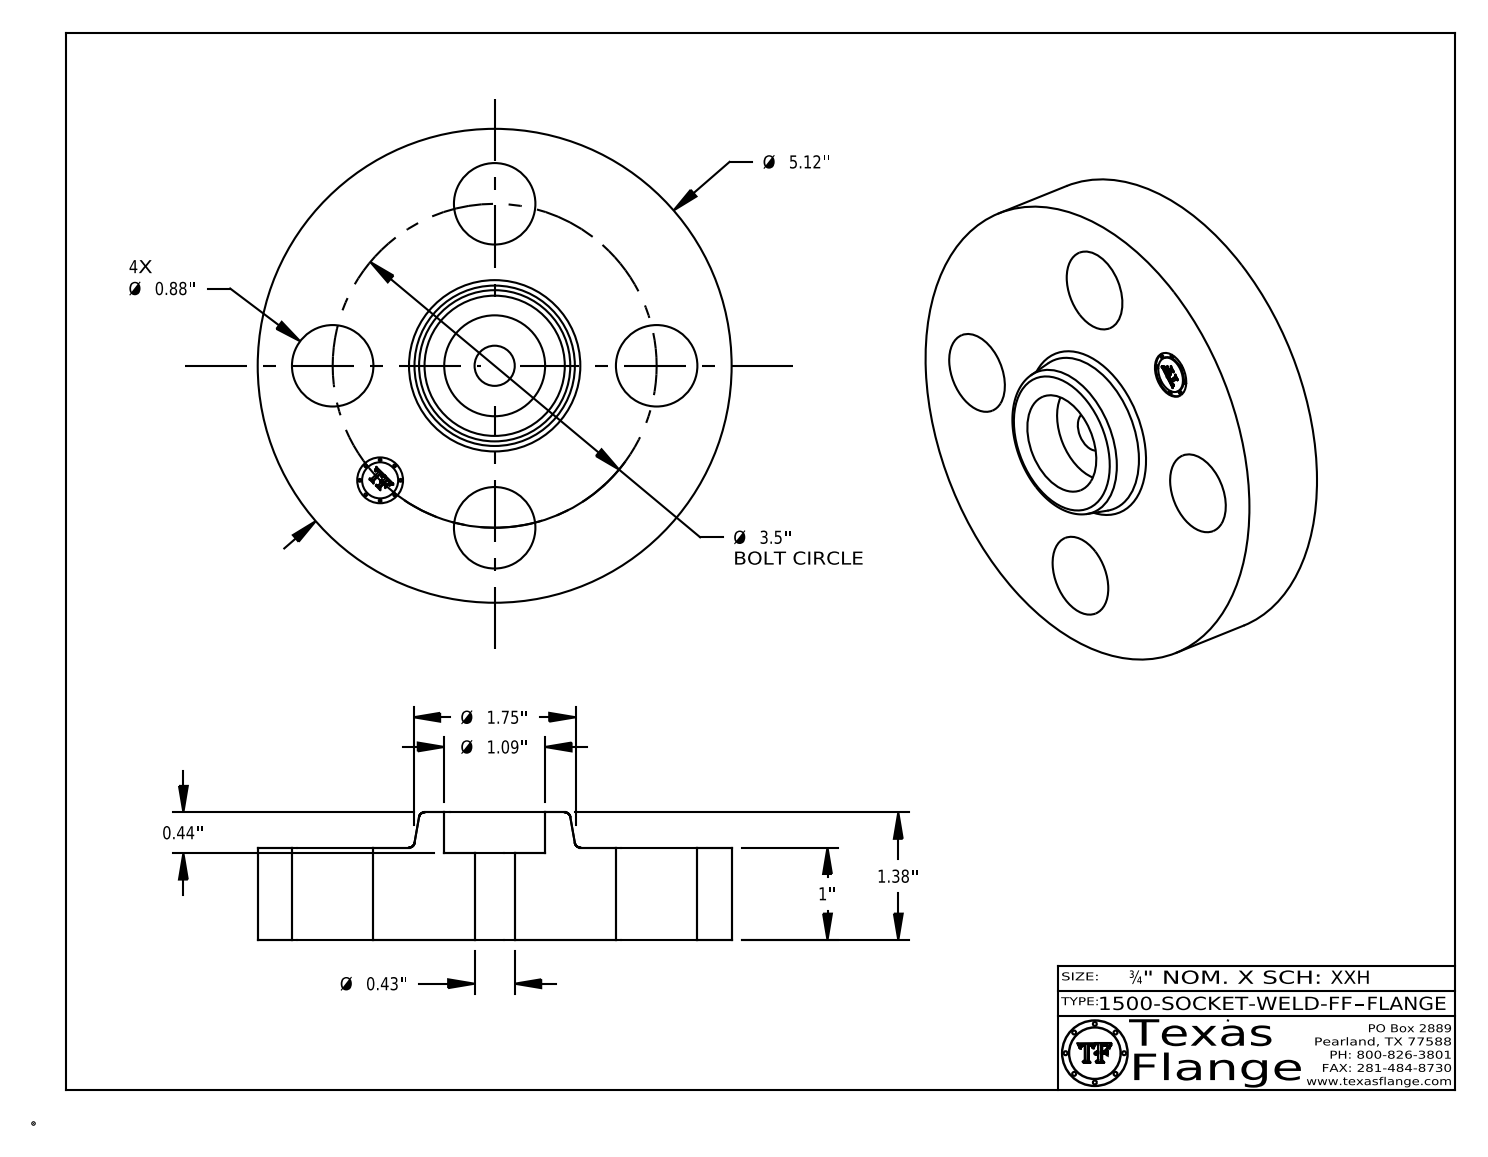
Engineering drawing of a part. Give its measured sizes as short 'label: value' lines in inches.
name: 1500-SOCKET-WELD-FF
written by: CATIA V5 STEP AP214 (AUTOMOTIVE_DESIGN)
unit: in
bodies: 1 solid, 409 faces (369 planar, 34 cylindrical, 6 other)
size: 5.12 × 5.12 × 1.38
volume: 18.45 in³; area: 67.55 in²
holes: 4× ⌀0.88, 1× ⌀0.434, 1× ⌀0.495, 1× ⌀1.09
bosses: 8× ⌀0.03, 1× ⌀5.12, 1× ⌀0.39
face distances: 1, 1.38, 0.38, 0.06, 0.94, 0.44, 0.015, 0.985, 0.045, 0.395
hole spacings: 1.75, 2.475, 1.339, 3.233, 3.5
